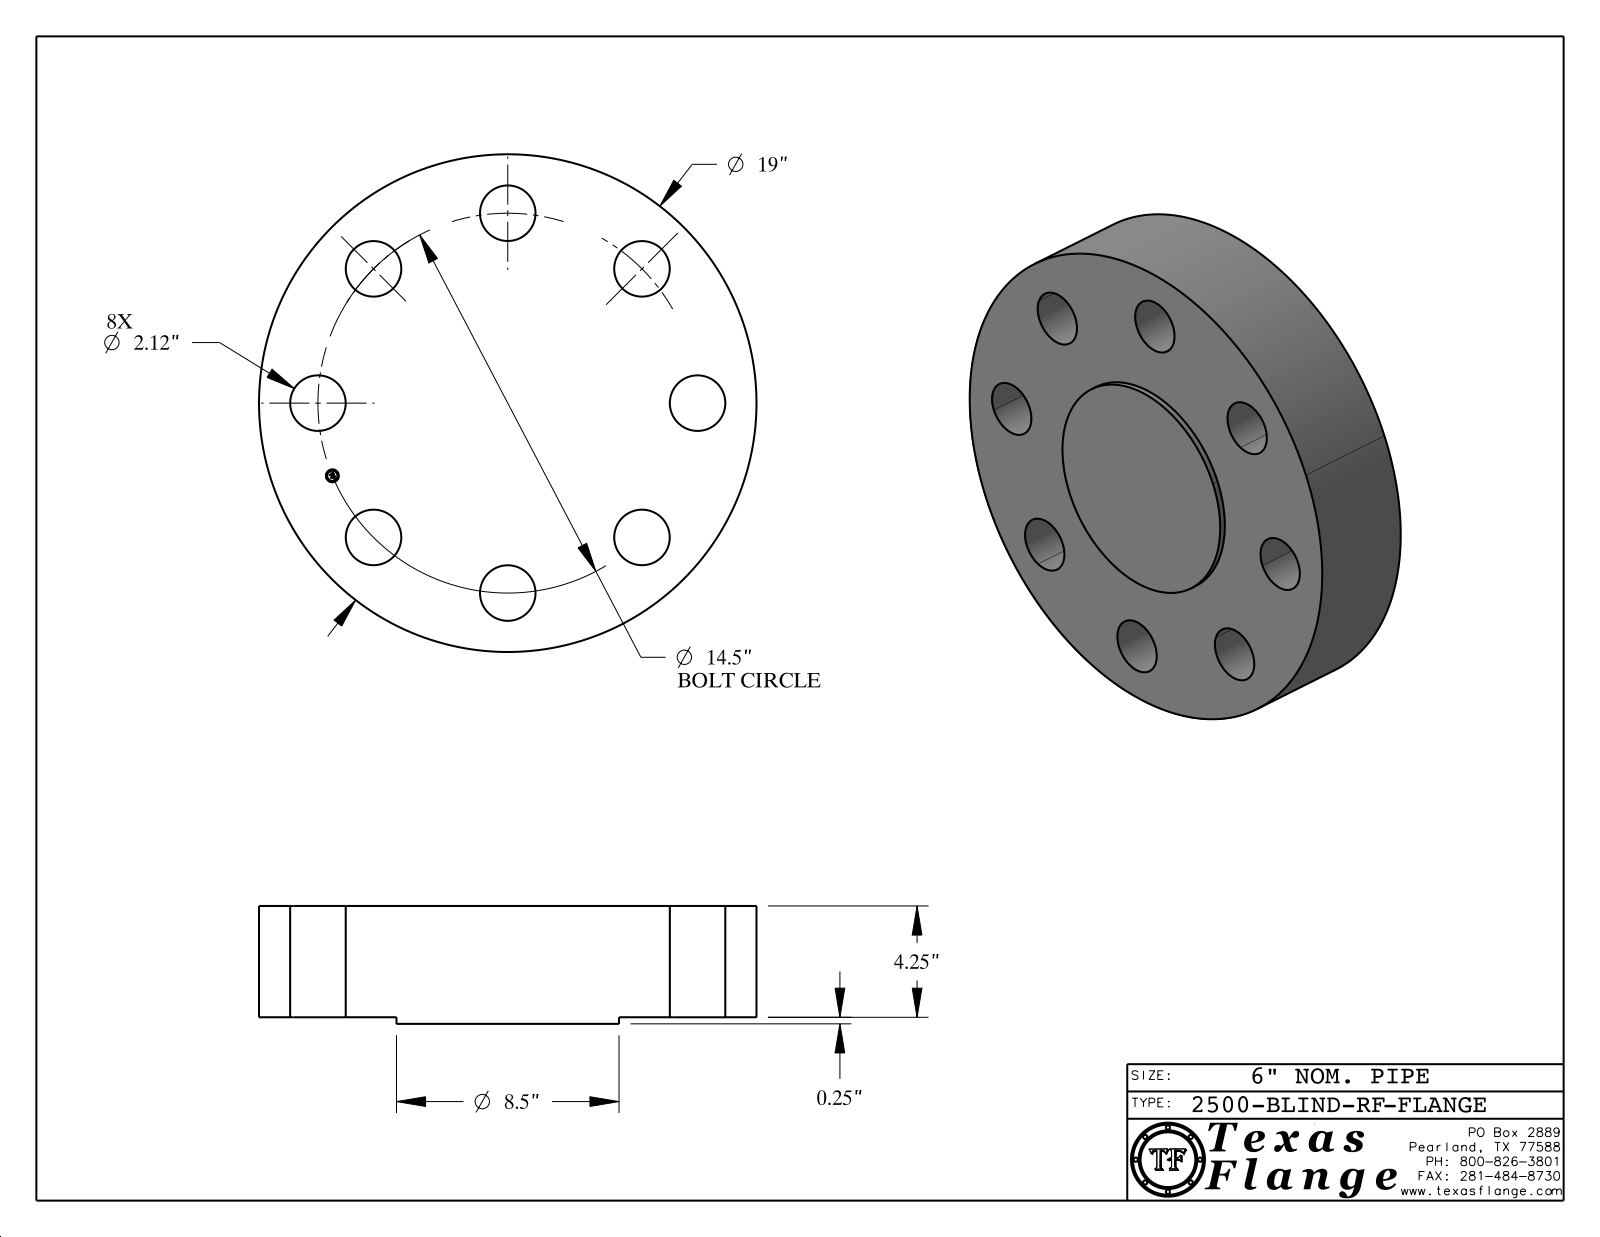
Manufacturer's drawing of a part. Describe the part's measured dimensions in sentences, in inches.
The part is named "2500-BLIND-RF". Its 3-D file was written by "CATIA V5 STEP AP214 (AUTOMOTIVE_DESIGN)". It is 1 solid with 408 faces: 368 planar, 40 cylindrical and 0 other. Overall it measures 19 by 19 by 4.5 inches. Its volume is 1 099 cubic inches and its surface area 997.5 square inches. Round holes: 8 of diameter 2.12, 1 of diameter 0.495. Round bosses or shafts: 8 of diameter 0.03, 1 of diameter 19, 1 of diameter 8.5, 1 of diameter 0.39. The main face-to-face distances are 4.25, 0.25, 4.5, 0.015, 4.485, 4.235, 0.148, 0.145, 0.027, 0.096. The hole center spacings are 5.549, 13.396, 10.253, 10.253, 2.829, 14.221, 14.5, 14.5.
